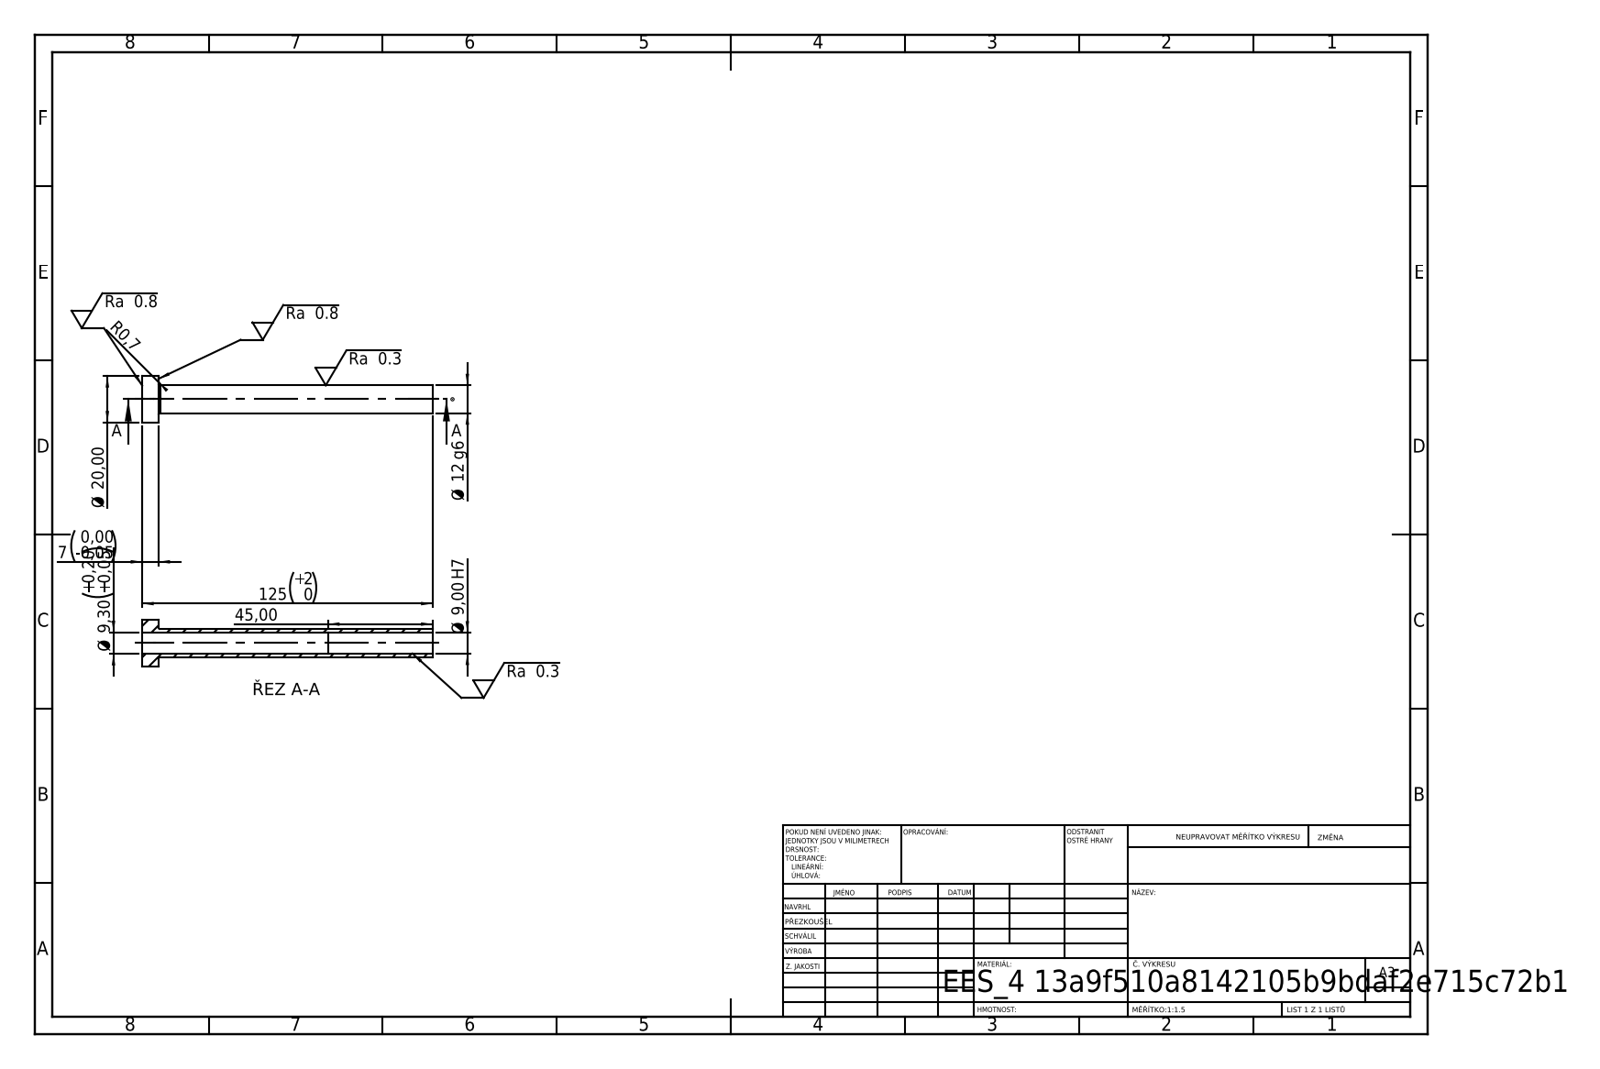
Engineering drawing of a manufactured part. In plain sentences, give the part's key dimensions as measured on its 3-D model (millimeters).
Its 3-D file was written by "SolidWorks 2019 (CONFIG_CONTROL_DESIGN)". It is 1 solid with 14 faces: 4 planar, 8 cylindrical and 2 other. Overall it measures 125 by 20 by 20 millimeters. Its volume is 7 252 cubic millimeters and its surface area 8 988 square millimeters. Round holes: 1 of diameter 9, 1 of diameter 9.3. Round bosses or shafts: 1 of diameter 20, 1 of diameter 12. The main face-to-face distances are 7, 125, 118, 80, 73, 45.
